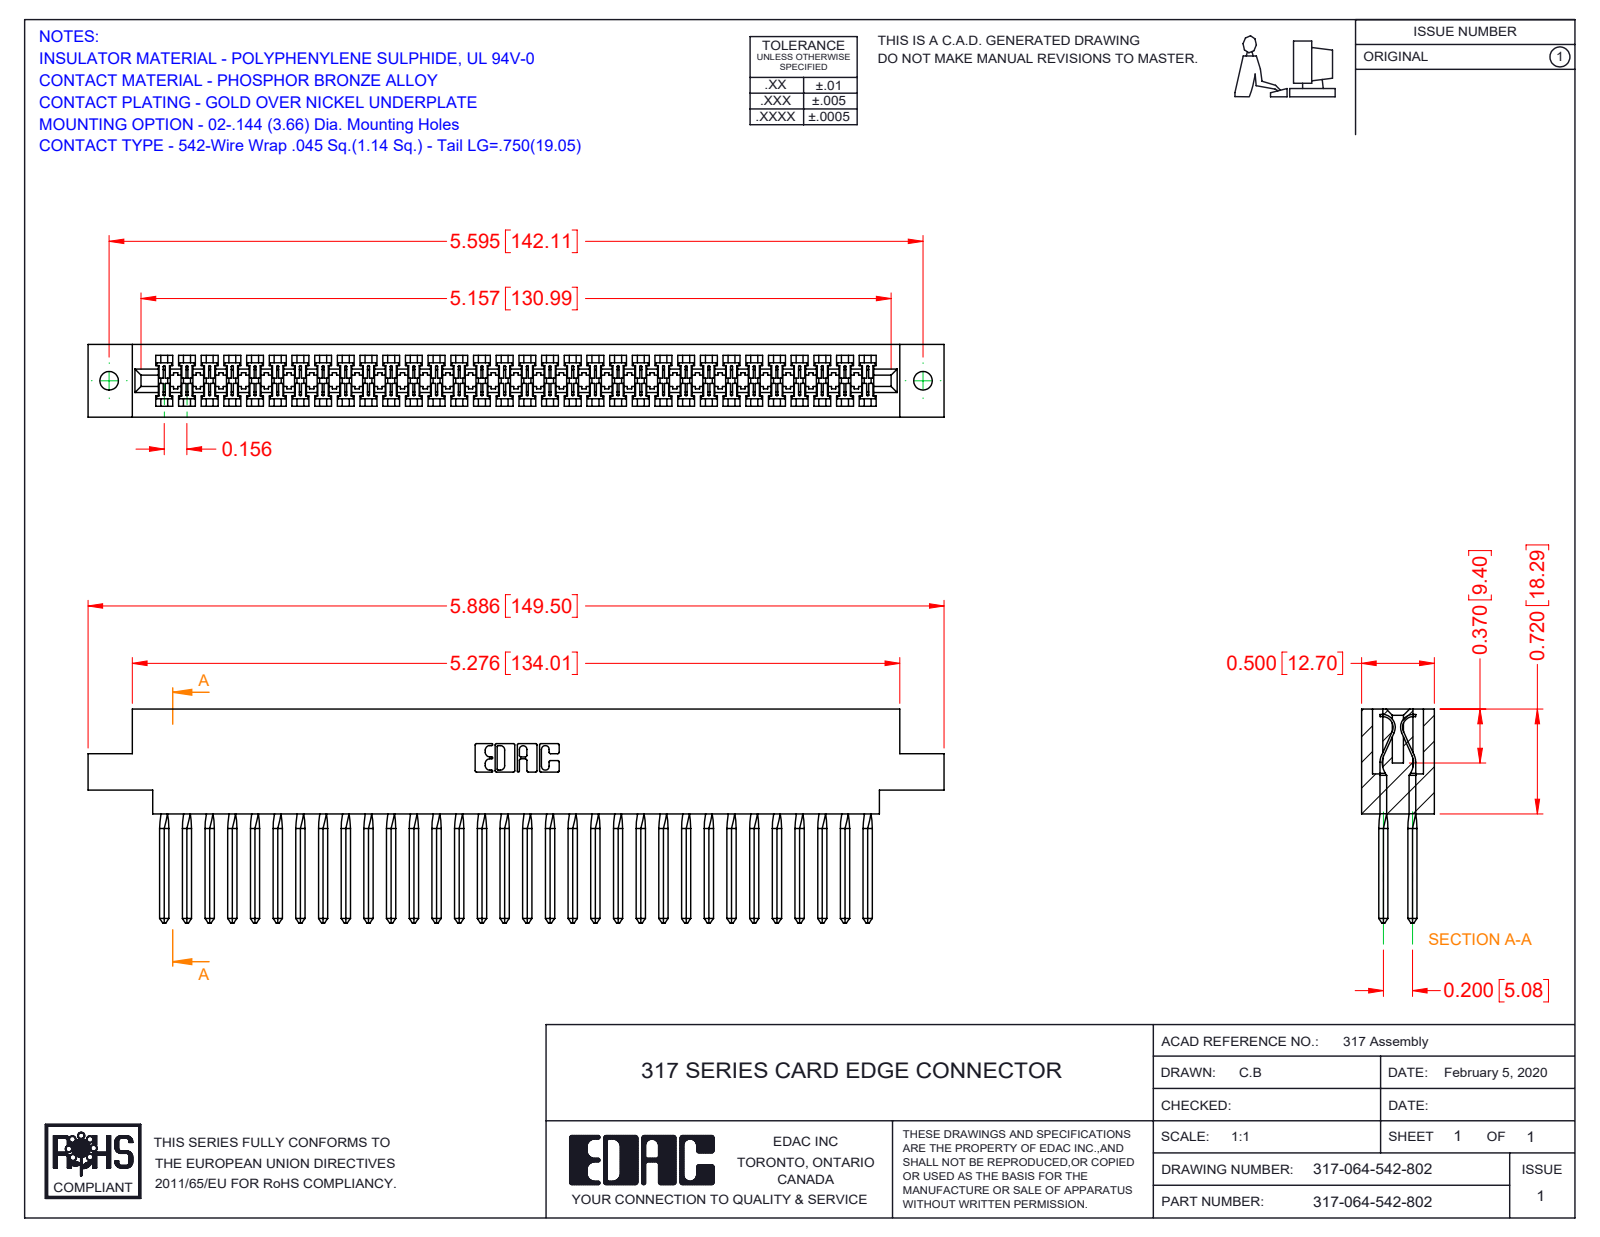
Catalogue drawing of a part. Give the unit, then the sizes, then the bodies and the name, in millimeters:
Units: millimetres
Overall size (bounding box): 149.5 × 37.3 × 12.7
Round holes (diameter × count): ⌀3.3 ×2
Partial cylindrical surfaces — rounded edges, fillets, slot ends (radius × count): R0.2 ×128, R0.3 ×22, R0.2 ×6, R0.8 ×6, R0.7 ×3, R1.9 ×2, R2.3 ×2, R2.5 ×2
Main face-to-face distances: 12.7, 1.9, 10.8, 8.9, 5.1, 2.9, 2.8, 1.2, 3.3, 9.4
Hole centre spacings: 142.1
Volume: 24 120 mm³ · Surface area: 32 970 mm²
Bodies: 65 solids, 3750 faces (3002 planar, 492 cylindrical, 256 other)
Part name (STEP PRODUCT): 317 Part_.144 Dia; 317-290-003_542; 317-064-542-802
STEP written by: SolidWorks 2016 (CONFIG_CONTROL_DESIGN)
